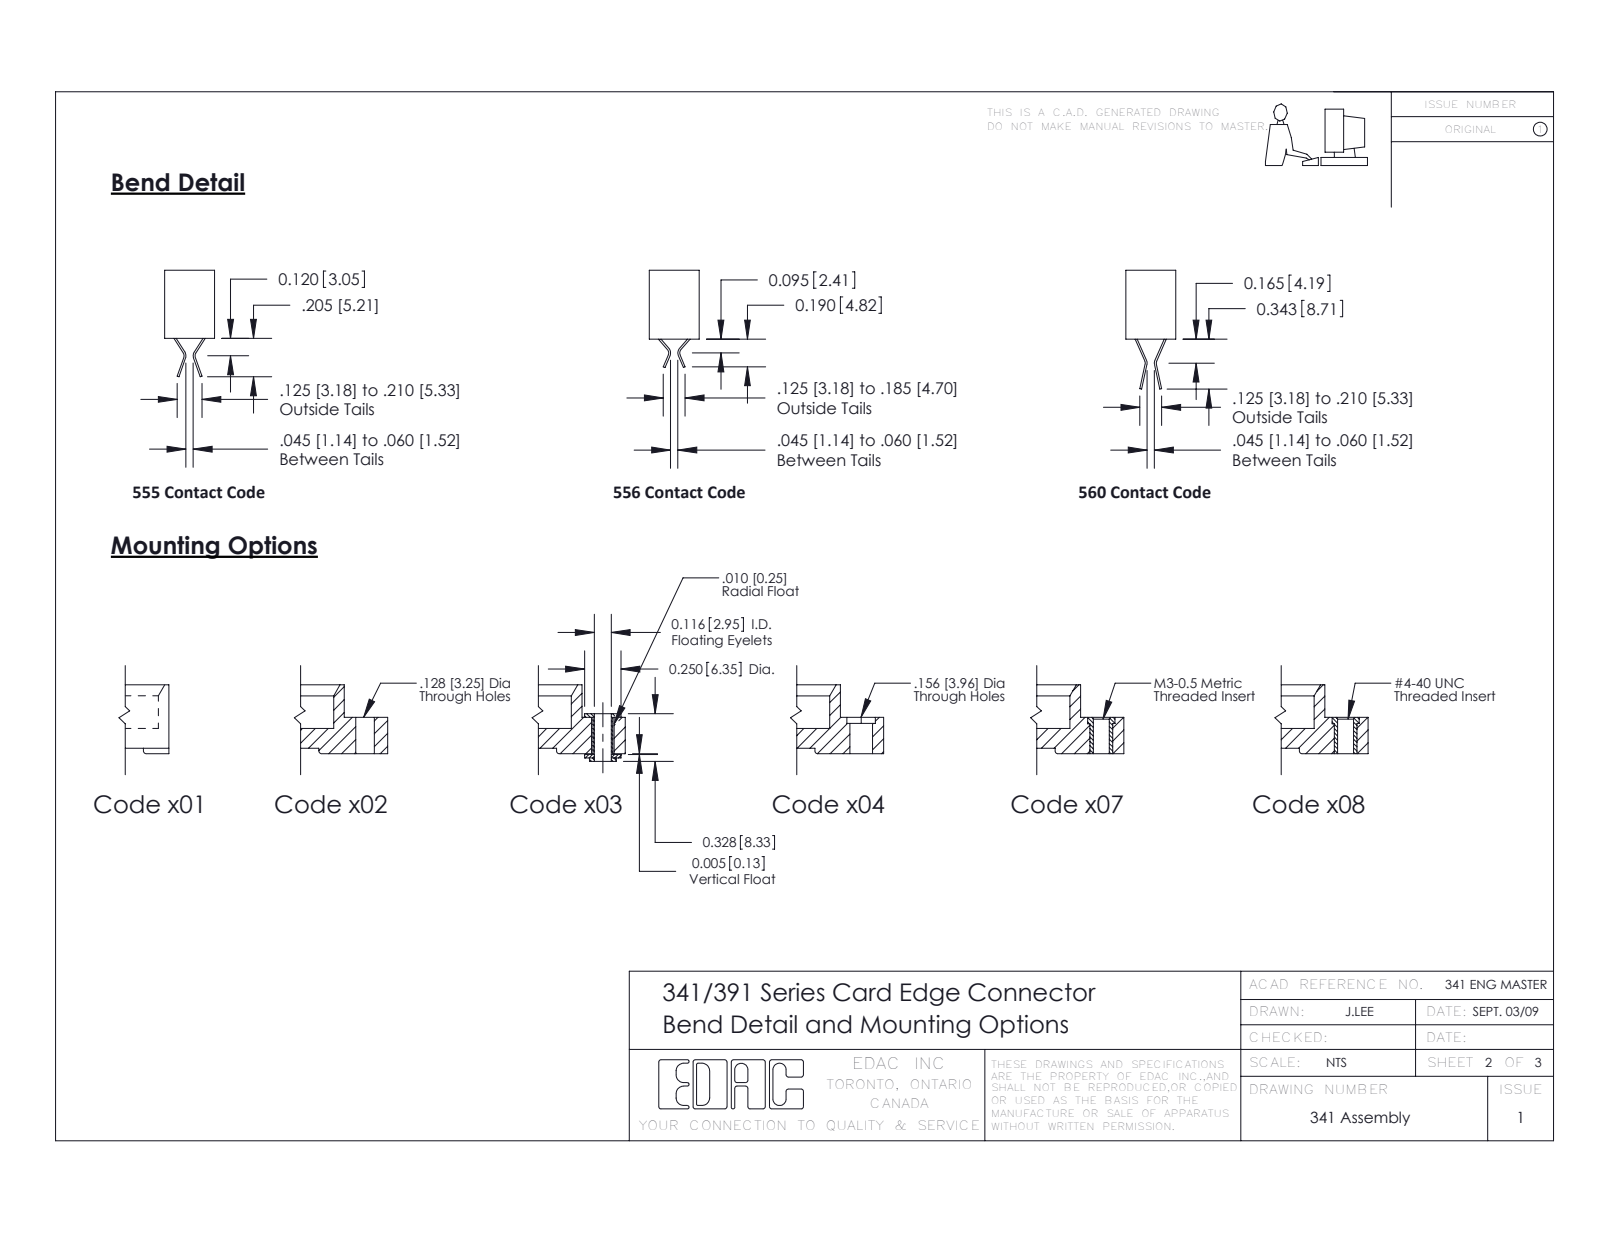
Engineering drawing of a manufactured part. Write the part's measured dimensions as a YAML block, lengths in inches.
part_name: "341 Part_.156 (3.96) Dia Mounting Holes; 341-292-001_341-292-121; 391-005-521-103; 345-250-002_345-250-002-102"
step_written_by: "SolidWorks 2016 (CONFIG_CONTROL_DESIGN)"
units: inches
bodies: {solids: 8, faces: 578, planar: 347, cylindrical: 203, other: 28}
overall_size: [1.375, 0.697, 0.33]
volume: 0.122
surface_area: 4.889
round_holes:
  - {diameter: 0.116, count: 2}
  - {diameter: 0.156, count: 2}
round_bosses_or_shafts:
  - {diameter: 0.25, count: 2}
  - {diameter: 0.18, count: 2}
  - {diameter: 0.136, count: 2}
partial_cylinders:
  - {radius: 0.015, count: 32}
  - {radius: 0.01, count: 22}
  - {radius: 0.02, count: 11}
  - {radius: 0.004, count: 10}
  - {radius: 0.007, count: 6}
  - {radius: 0.031, count: 6}
  - {radius: 0.013, count: 5}
  - {radius: 0.026, count: 3}
face_to_face_distances: [0.1, 0.33, 0.2, 0.3, 0.056, 0.156, 0.044, 0.031, 0.25, 0.041]
hole_center_spacings: [1.075]
